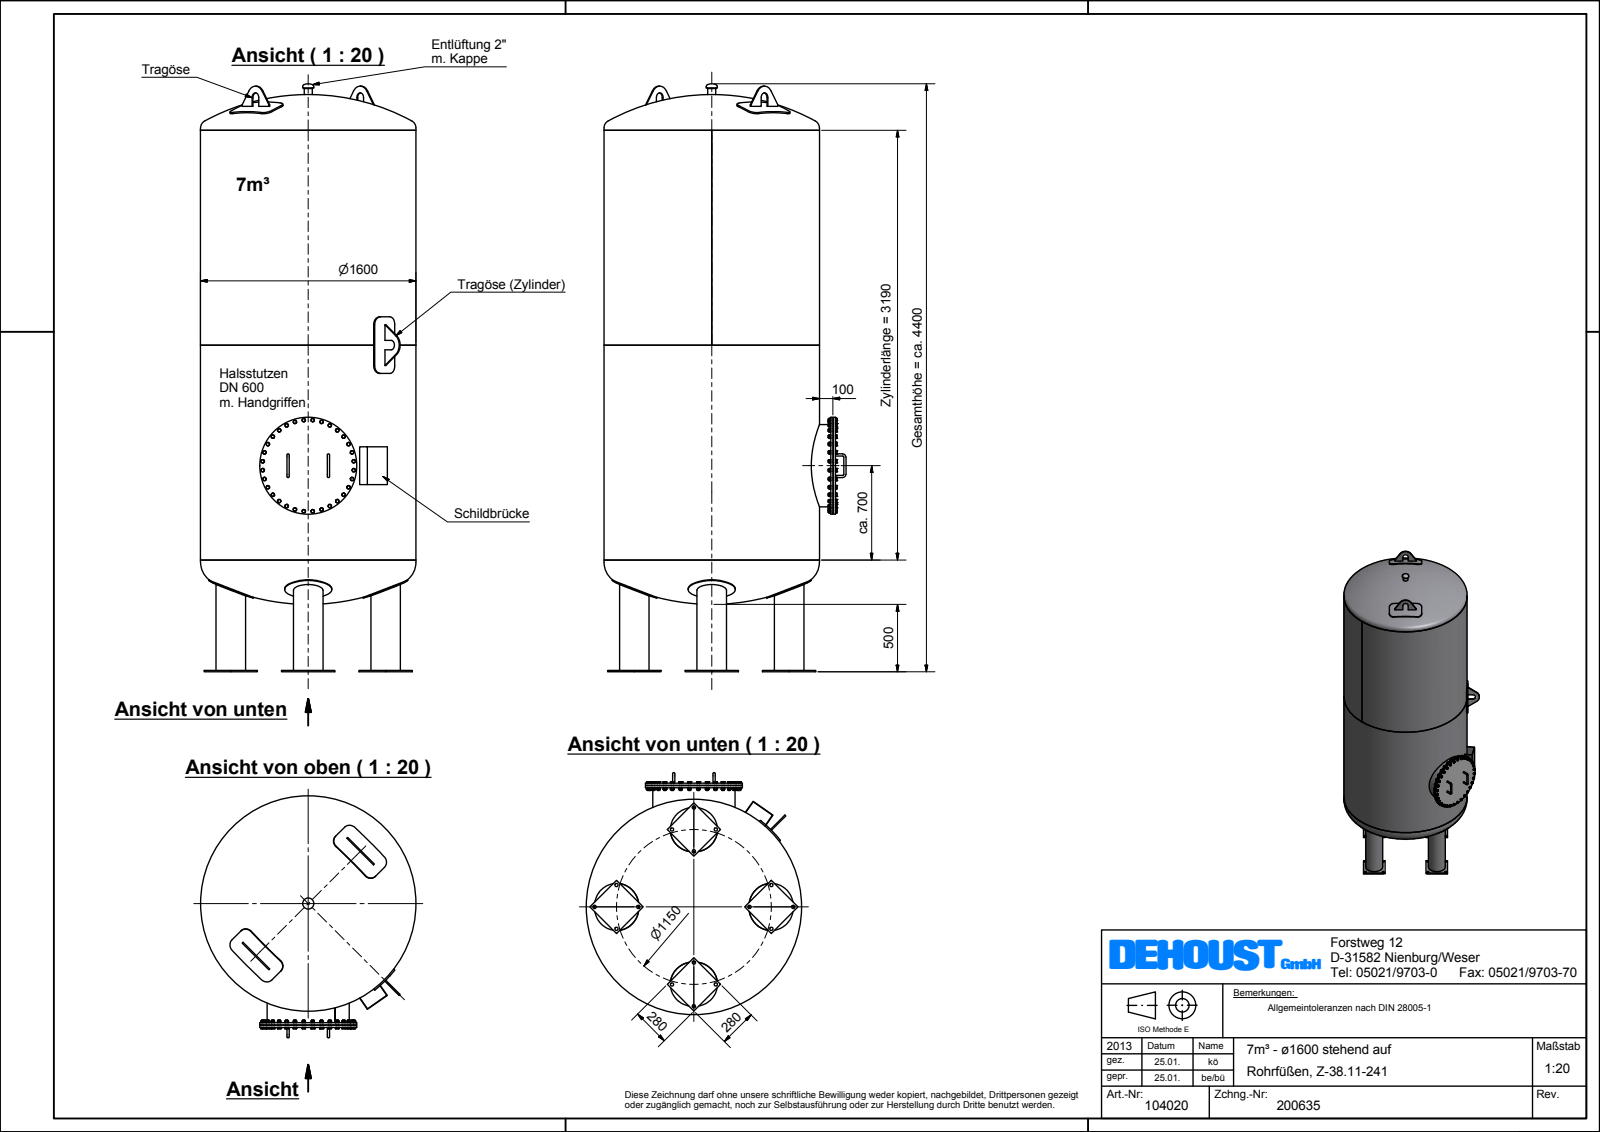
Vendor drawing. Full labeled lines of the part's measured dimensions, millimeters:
Part name (STEP PRODUCT): Beh\S\dlter_Z-38_11-241_1600_007_KV
STEP written by: Autodesk Inventor 2012 (AUTOMOTIVE_DESIGN)
Units: millimetres
Bodies: 2 solids, 1075 faces (610 planar, 151 cylindrical, 314 other)
Overall size (bounding box): 4365.54 × 1797 × 1600
Volume: 570 600 000 mm³ · Surface area: 47 310 000 mm²
Round holes (diameter × count): ⌀209.1 ×4, ⌀598 ×1, ⌀1590 ×1
Round bosses / shafts (diameter × count): ⌀16 ×38, ⌀22.5 ×32, ⌀350 ×4, ⌀219.1 ×4, ⌀1600 ×1, ⌀720 ×1, ⌀660 ×1, ⌀610 ×1
Partial cylindrical surfaces — rounded edges, fillets, slot ends (radius × count): R56 ×12, R35 ×3, R85 ×3, R810 ×1
Main face-to-face distances: 35, 10, 830.07, 820.07, 16, 19, 3, 2.93, 549.42, 559.42
Hole centre spacings: 575, 813.17, 1150
